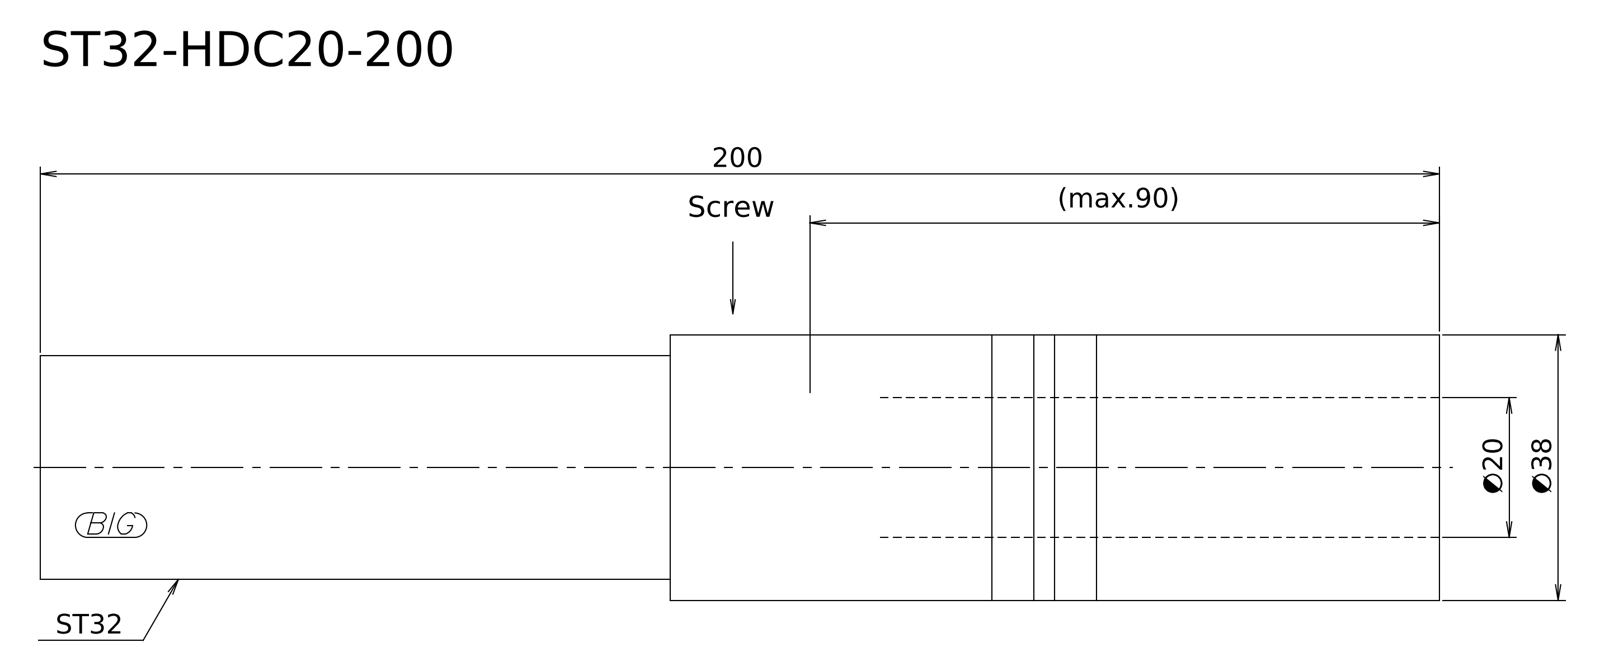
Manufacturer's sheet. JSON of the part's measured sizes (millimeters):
{"step_written_by": "Kubotek KeyCreator V8.5.1 (14335) (CONFIG_CONTROL_DESIGN)", "units": "millimeters", "bodies": {"solids": 1, "faces": 5, "planar": 3, "cylindrical": 2, "other": 0}, "overall_size": [200, 38, 38], "volume_mm3": 197135, "surface_area_mm2": 24448, "round_bosses_or_shafts": [[38, 1], [32, 1]], "face_to_face_distances": [200, 110, 90]}
